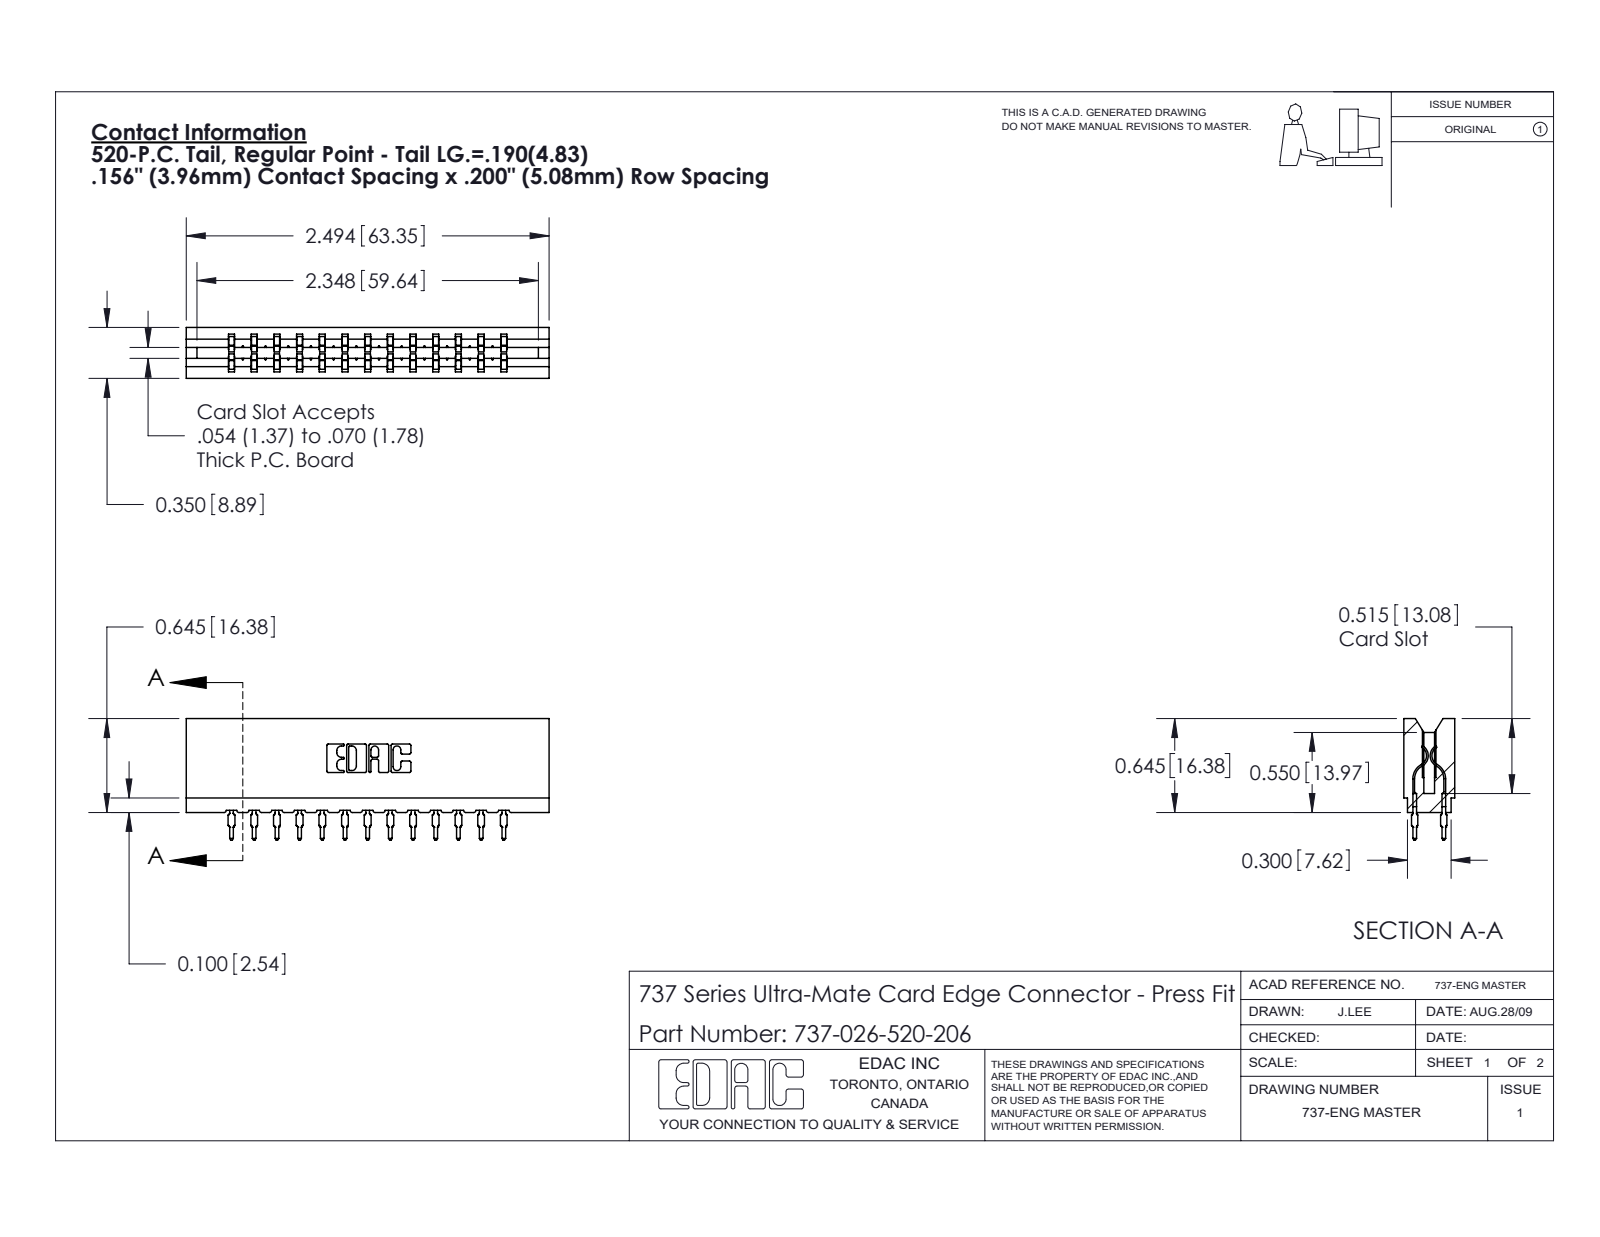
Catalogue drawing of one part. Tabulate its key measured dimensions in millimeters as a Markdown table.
| quantity | value |
| --- | --- |
| part name | 737-026-520-206; 745-292-001_520; 737 Part_Insulator Option - 06 |
| STEP written by | SolidWorks 2020 (CONFIG_CONTROL_DESIGN) |
| units | millimeters |
| bodies | 27 solids, 2435 faces (1264 planar, 495 cylindrical, 676 other) |
| overall size | 63.3 × 21.2 × 8.9 |
| volume | 6 410 mm³ |
| surface area | 8 535 mm² |
| partial cylindrical surfaces (radius × count) | 0.5 × 52, 0.4 × 26, 0.3 × 22, 0.1 × 8, 0.3 × 8, 0.2 × 6, 0.8 × 6, 0.7 × 3 |
| main face-to-face distances | 3.5, 5.4, 8.9, 4, 15.8, 19.8, 11.9, 7.9, 1.9, 1.6 |
